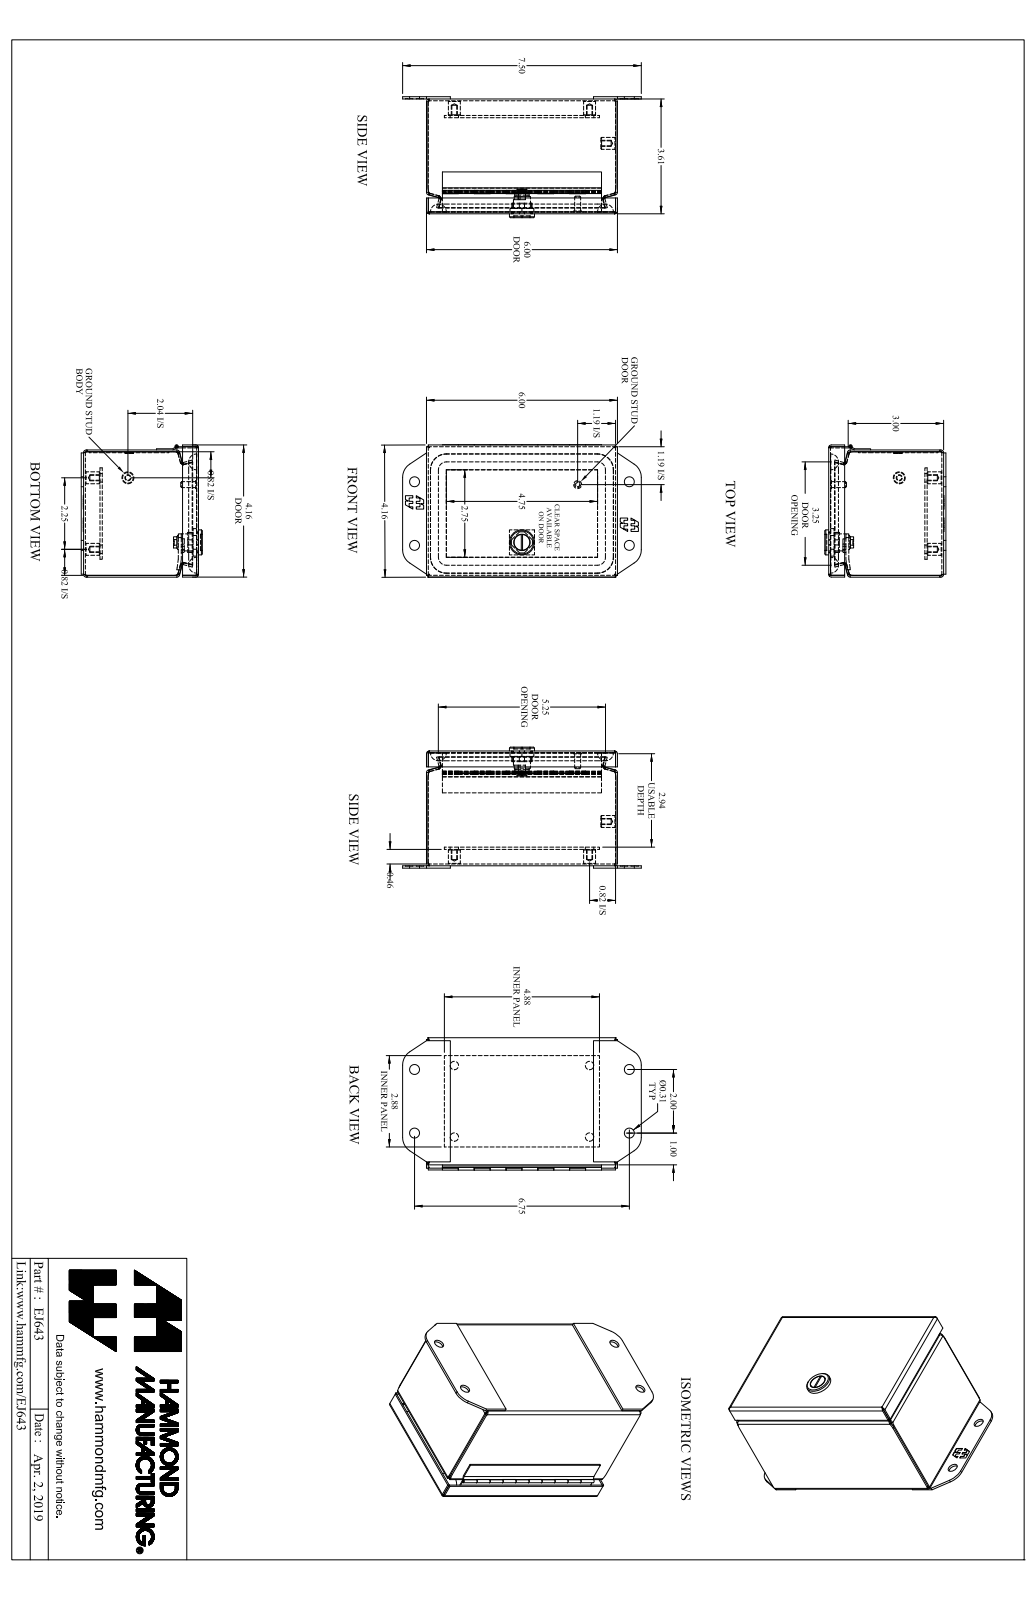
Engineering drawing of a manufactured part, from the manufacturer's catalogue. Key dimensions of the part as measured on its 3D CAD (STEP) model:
Part name (STEP PRODUCT): EJ643_Default
STEP written by: SolidWorks 2019 (CONFIG_CONTROL_DESIGN)
Units: inches
Bodies: 16 solids, 611 faces (345 planar, 174 cylindrical, 92 other)
Overall size (bounding box): 7.5 × 4.165 × 3.805
Volume: 11.31 in³ · Surface area: 371 in²
Round holes (diameter × count): ⌀0.156 ×5, ⌀0.265 ×4, ⌀0.313 ×4, ⌀0.05 ×1, ⌀0.516 ×1
Round bosses / shafts (diameter × count): ⌀0.375 ×5, ⌀0.788 ×1, ⌀0.535 ×1, ⌀0.496 ×1, ⌀0.435 ×1, ⌀0.25 ×1, ⌀0.188 ×1, ⌀0.1 ×1
Partial cylindrical surfaces — rounded edges, fillets, slot ends (radius × count): R0.029 ×16, R0.086 ×16, R0.281 ×10, R0.25 ×4, R0.499 ×4, R0.5 ×4, R0.06 ×2, R0.539 ×2
Main face-to-face distances: 0.057, 3.554, 3.943, 5.943, 0.072, 0.589, 3.611, 3.497, 3.886, 4
Hole centre spacings: 1.256, 5.501, 2, 2.136, 2.25, 2.465, 2.466, 2.94
